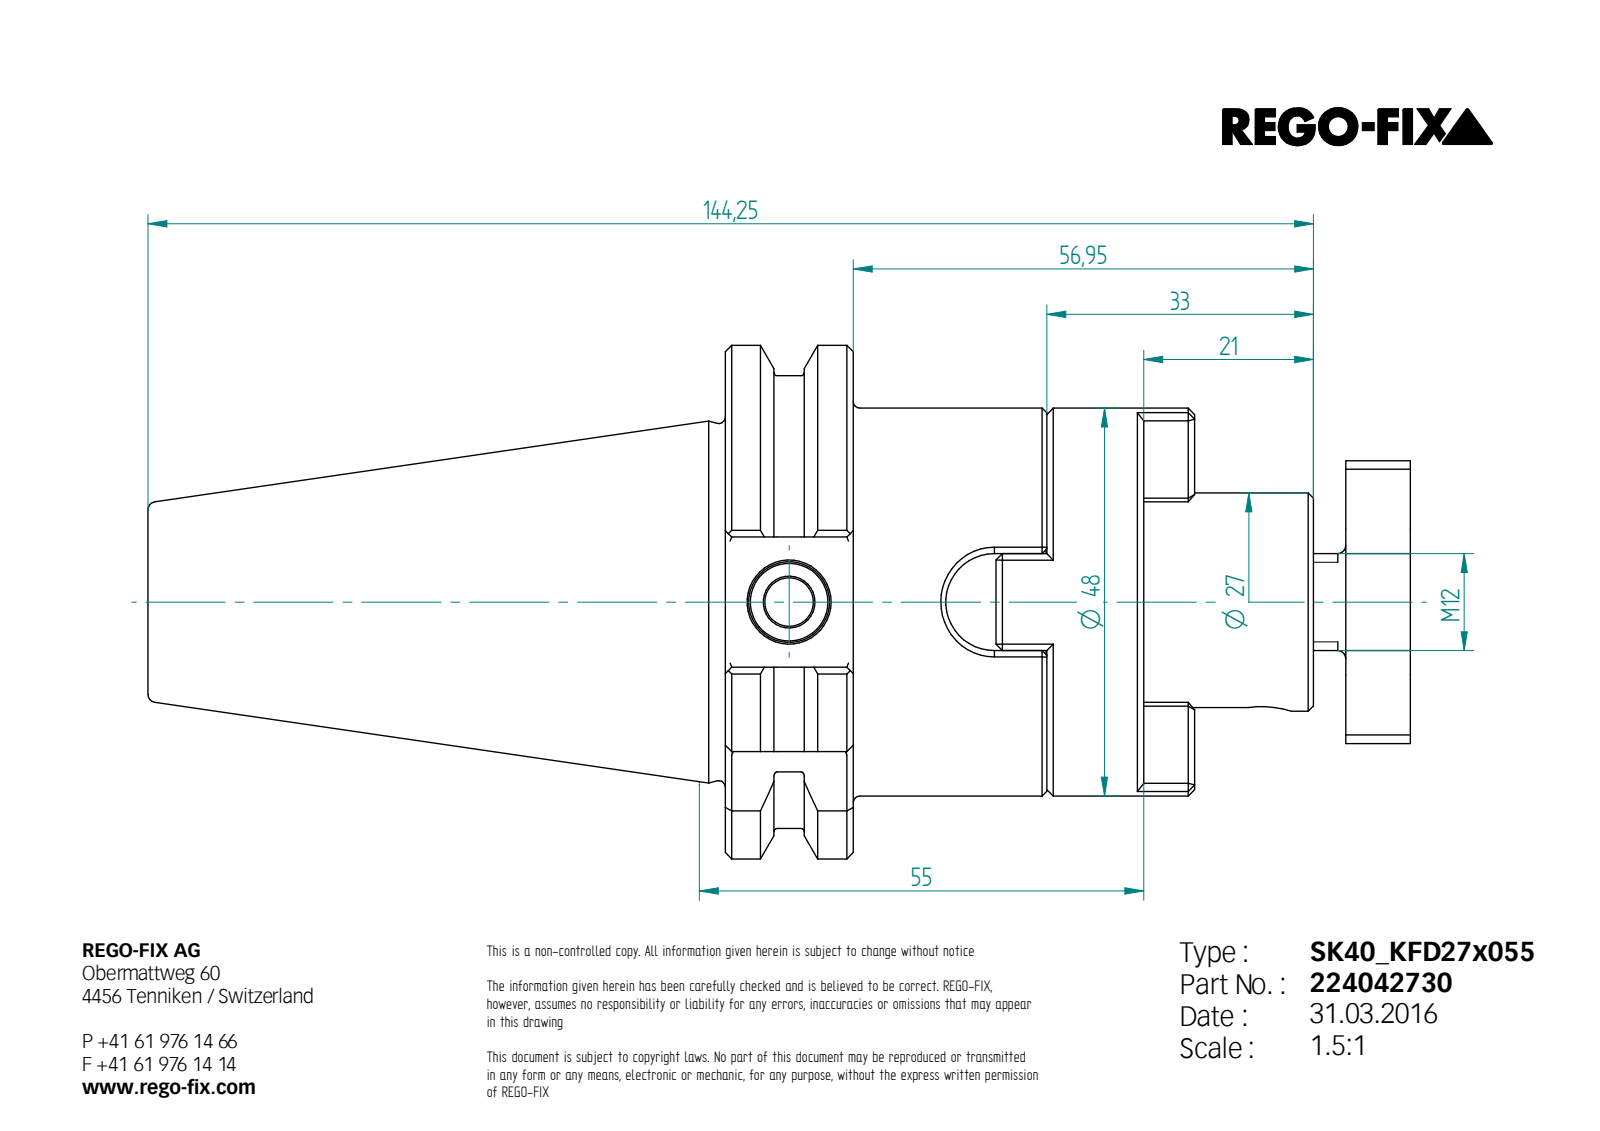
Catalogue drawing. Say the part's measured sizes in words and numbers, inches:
Its 3-D file was written by "Unknown (AUTOMOTIVE_DESIGN)". It is 3 solids with 245 faces: 128 planar, 49 cylindrical and 68 other. Overall it measures 6.152 by 2.502 by 2.402 inches. Its volume is 10.93 cubic inches and its surface area 59.45 square inches. Round holes: 1 of diameter 0.236, 1 of diameter 0.394, 1 of diameter 0.398, 1 of diameter 0.512, 1 of diameter 0.545, 1 of diameter 0.669, 1 of diameter 1.063. Round bosses or shafts: 1 of diameter 1.89, 1 of diameter 1.039, 1 of diameter 0.472. Partial cylindrical surfaces (rounded edges, fillets, slot ends): 11 of radius 0.02, 4 of radius 0.118, 2 of radius 0.138, 1 of radius 0.236, 1 of radius 0.317, 1 of radius 0.689, 1 of radius 1.102, 1 of radius 1.251. The main face-to-face distances are 0.472, 1.567, 1.299, 0.624, 0.943, 2.039, 1.415, 0.315, 3.339, 2.715.
